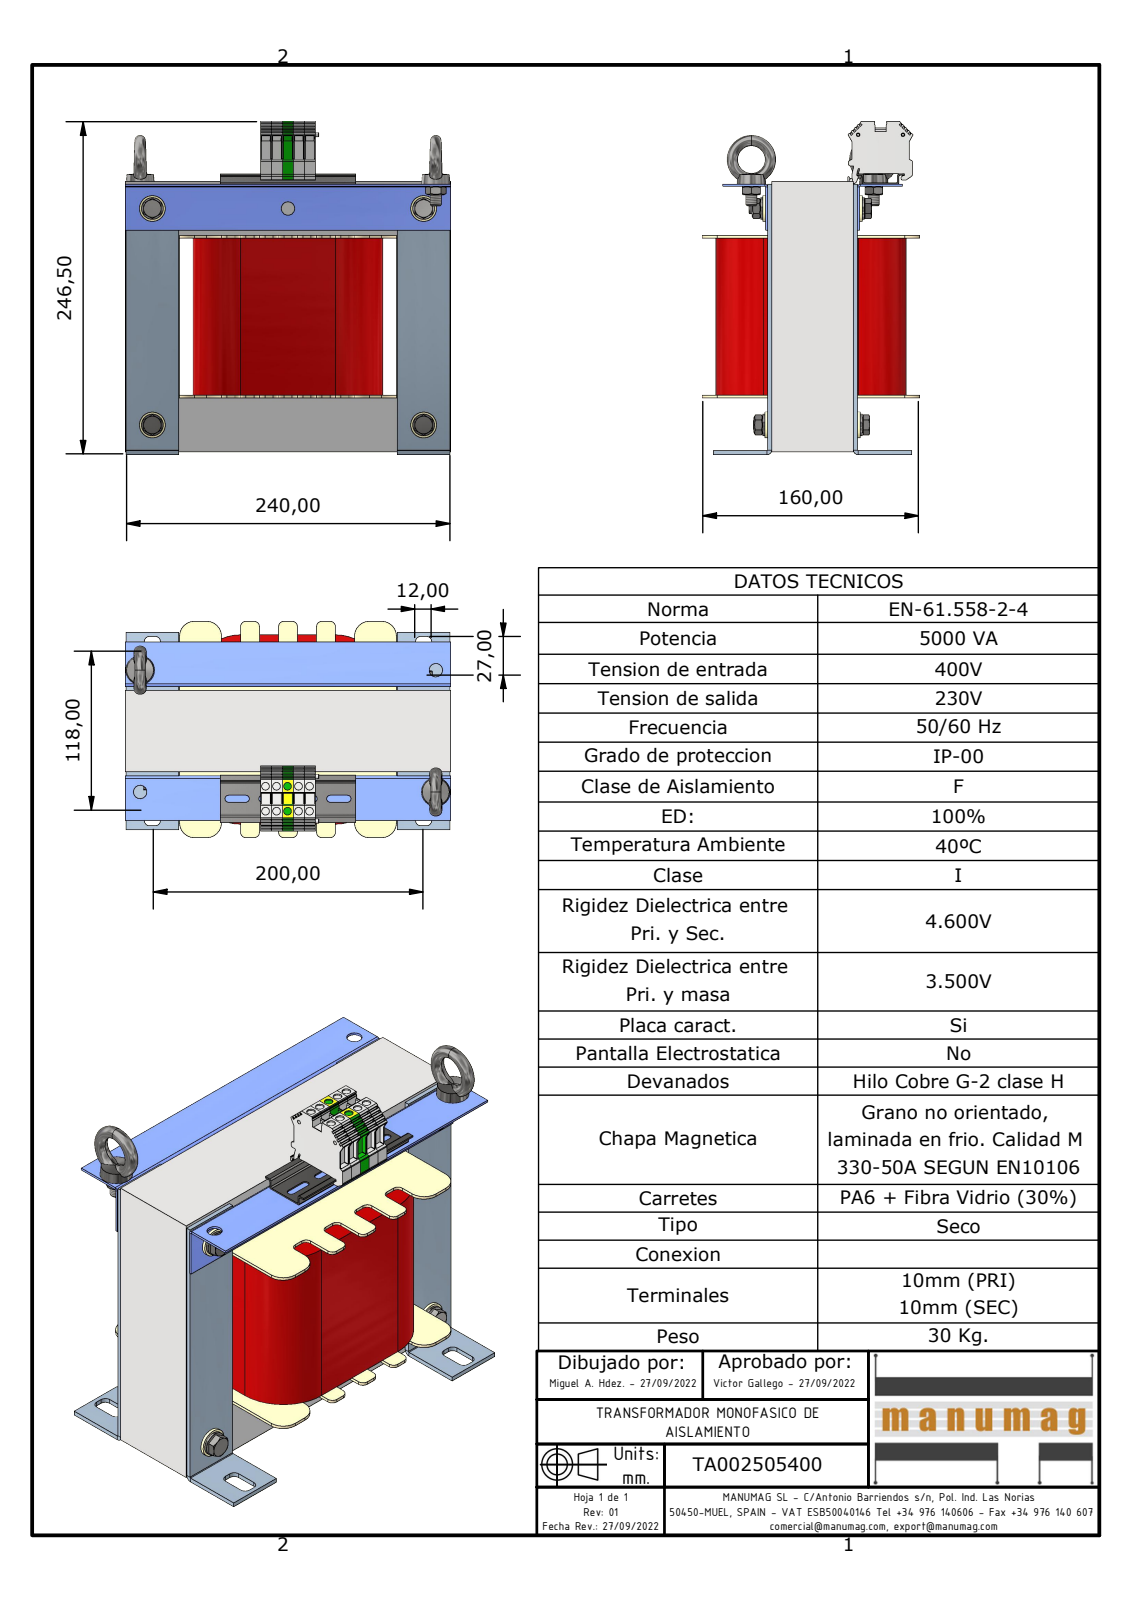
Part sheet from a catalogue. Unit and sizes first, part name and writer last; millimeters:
Units: millimetres
Overall size (bounding box): 246.5 × 240 × 160
Round holes (diameter × count): ⌀5.7 ×10, ⌀10 ×7, ⌀6.65 ×6, ⌀8 ×4, ⌀8.4 ×4, ⌀11 ×4, ⌀12 ×4, ⌀2.4 ×2, ⌀2.5 ×2, ⌀2.75 ×2
Round bosses / shafts (diameter × count): ⌀19 ×4, ⌀16 ×4, ⌀11.4 ×4, ⌀9.6 ×4, ⌀7.32 ×4, ⌀8 ×2, ⌀5.82 ×2
Partial cylindrical surfaces — rounded edges, fillets, slot ends (radius × count): R0.3 ×57, R4 ×44, R1 ×14, R0.4 ×8, R0.5 ×8, R2.6 ×8, R11 ×8, R2 ×7
Main face-to-face distances: 40, 160, 60, 3, 63, 80, 2, 120, 200, 1.5
Hole centre spacings: 8.1, 20.1, 16.2, 24.52, 18.4, 24.3, 30.48, 32.4
Volume: 4 210 000 mm³ · Surface area: 535 075 mm²
Bodies: 42 solids, 1963 faces (1282 planar, 539 cylindrical, 142 other)
Part name (STEP PRODUCT): TA002505400; EI240 240 x 200 - 60 (Rc80); Escuadra RC80; SEMI 30 X 60 RC80 EI240 - 30 (+8 more)
STEP written by: Autodesk Inventor 2023 (AUTOMOTIVE_DESIGN)
